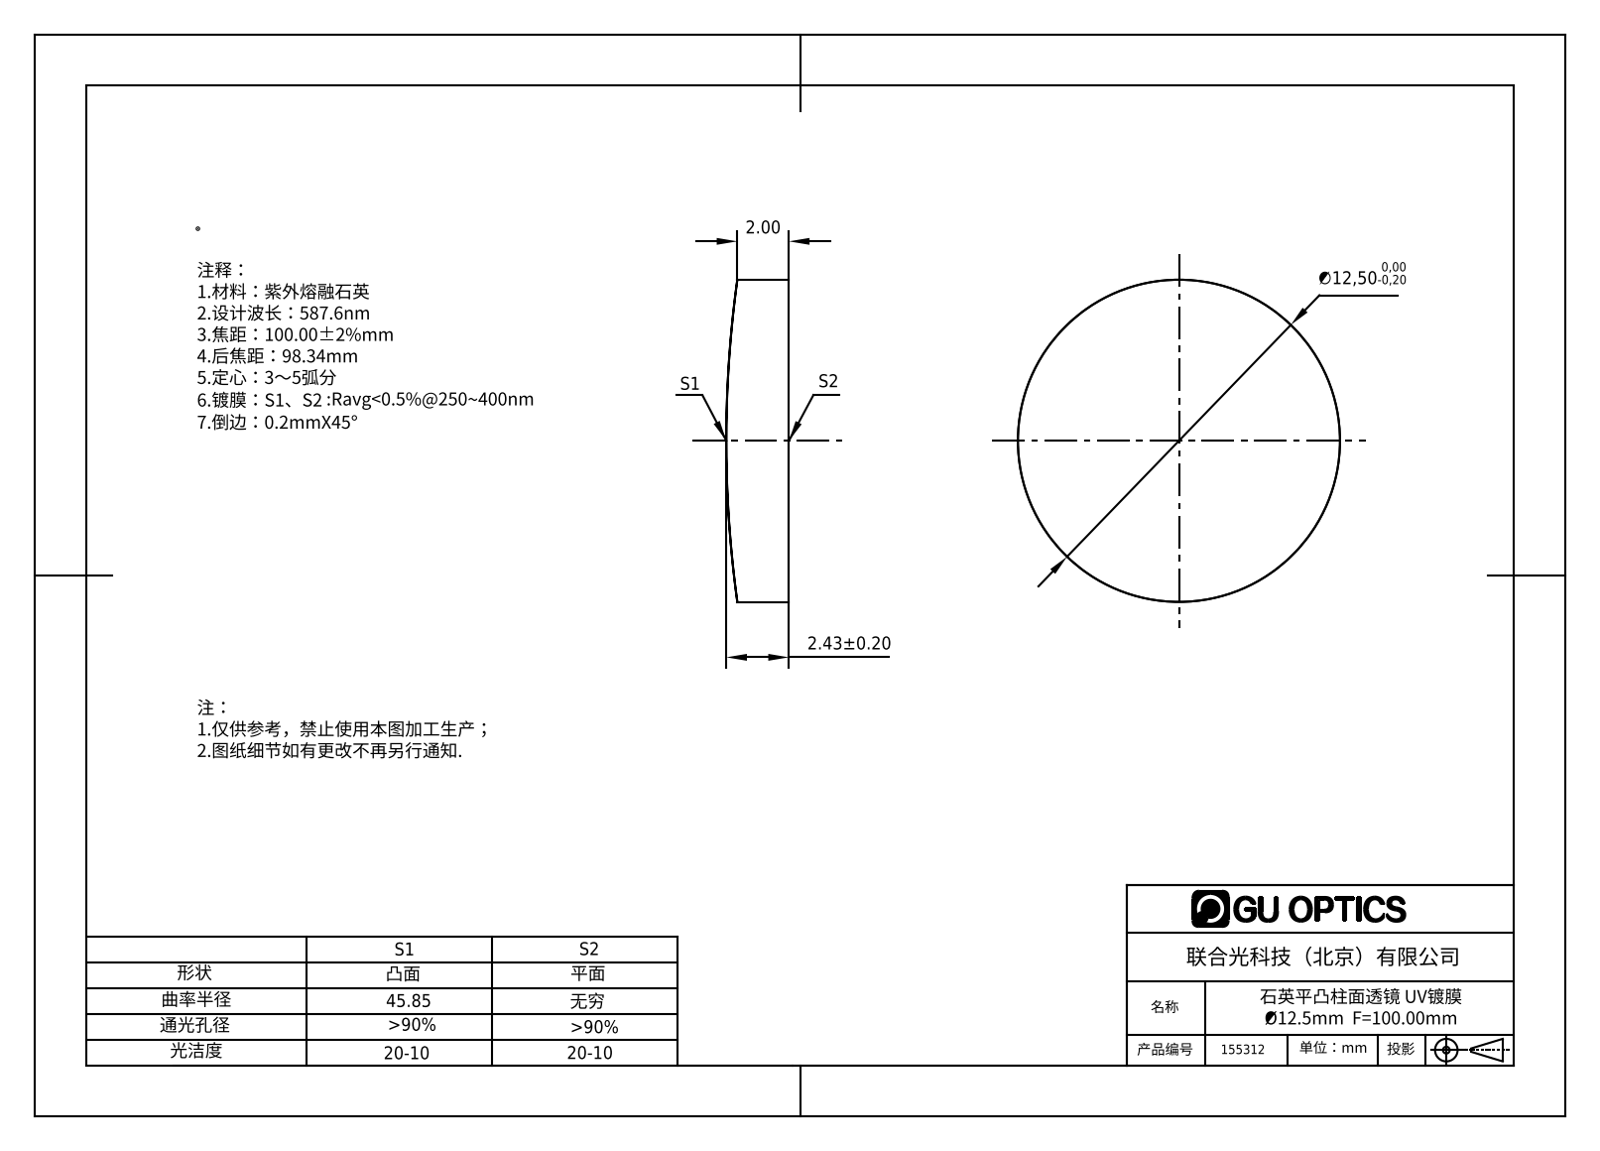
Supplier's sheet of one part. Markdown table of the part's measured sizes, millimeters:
| quantity | value |
| --- | --- |
| part name | 155278 |
| STEP written by | SolidWorks 2016 (AUTOMOTIVE_DESIGN) |
| units | millimeters |
| bodies | 1 solid, 4 faces (1 planar, 3 cylindrical, 0 other) |
| overall size | 12.5 × 12.5 × 2.43 |
| volume | 285 mm³ |
| surface area | 333 mm² |
| round bosses / shafts (diameter × count) | 12.5 × 1 |
| partial cylindrical surfaces (radius × count) | 45.85 × 1 |
